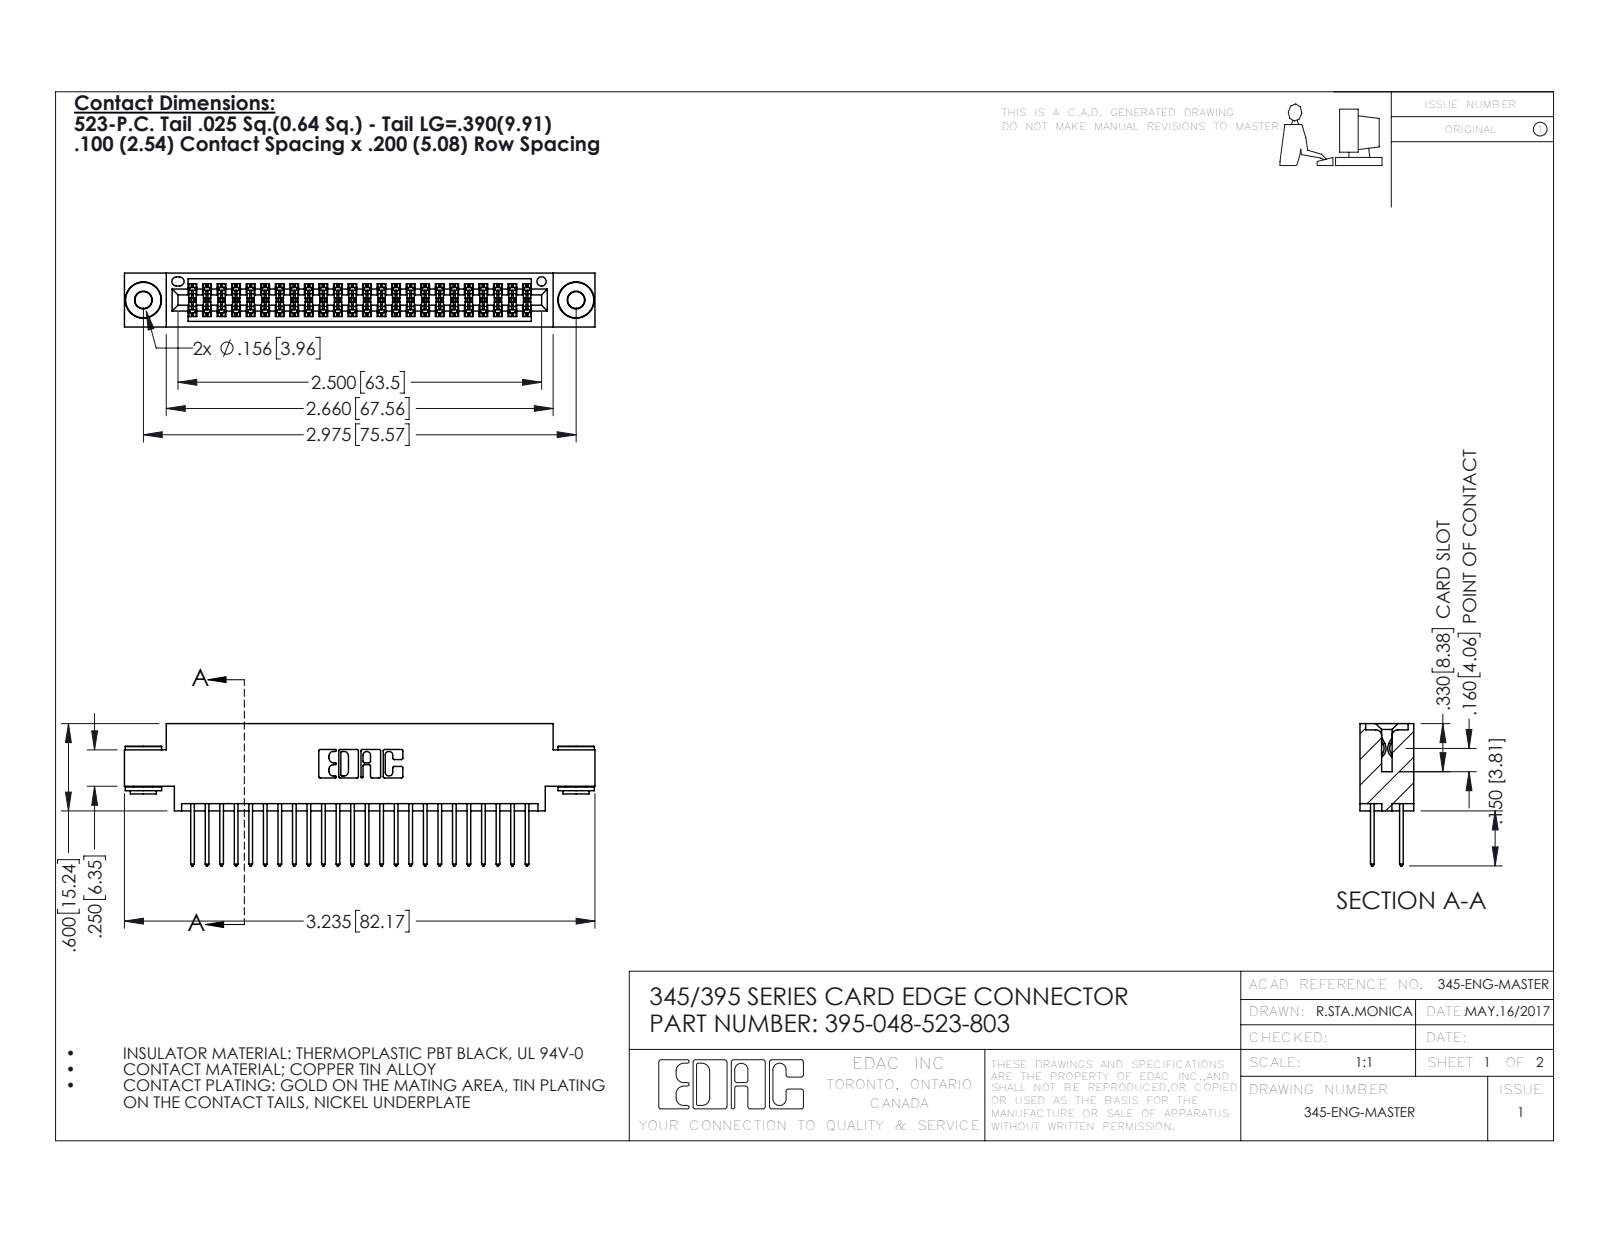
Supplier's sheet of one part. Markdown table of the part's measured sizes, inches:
| quantity | value |
| --- | --- |
| part name | 345-250-002_345-250-002-102; 395-048-523-803; 345 Part_0.170 Offset - 0.156 Dia-TH; 345-292-001_345-293-123 |
| STEP written by | SolidWorks 2016 (CONFIG_CONTROL_DESIGN) |
| units | inches |
| bodies | 51 solids, 2568 faces (1678 planar, 882 cylindrical, 8 other) |
| overall size | 3.235 × 0.977 × 0.37 |
| volume | 0.477 in³ |
| surface area | 18.6 in² |
| round holes (diameter × count) | 0.116 × 2, 0.156 × 2, 0.064 × 1 |
| round bosses / shafts (diameter × count) | 0.25 × 2, 0.18 × 2, 0.136 × 2 |
| partial cylindrical surfaces (radius × count) | 0.006 × 72, 0.01 × 48, 0.01 × 22, 0.007 × 6, 0.031 × 6, 0.026 × 3, 0.014 × 2, 0.019 × 2 |
| main face-to-face distances | 0.072, 0.298, 0.2, 0.37, 0.098, 0.272, 0.025, 0.225, 0.175, 0.15 |
| hole center spacings | 0.27, 2.741, 2.975 |
